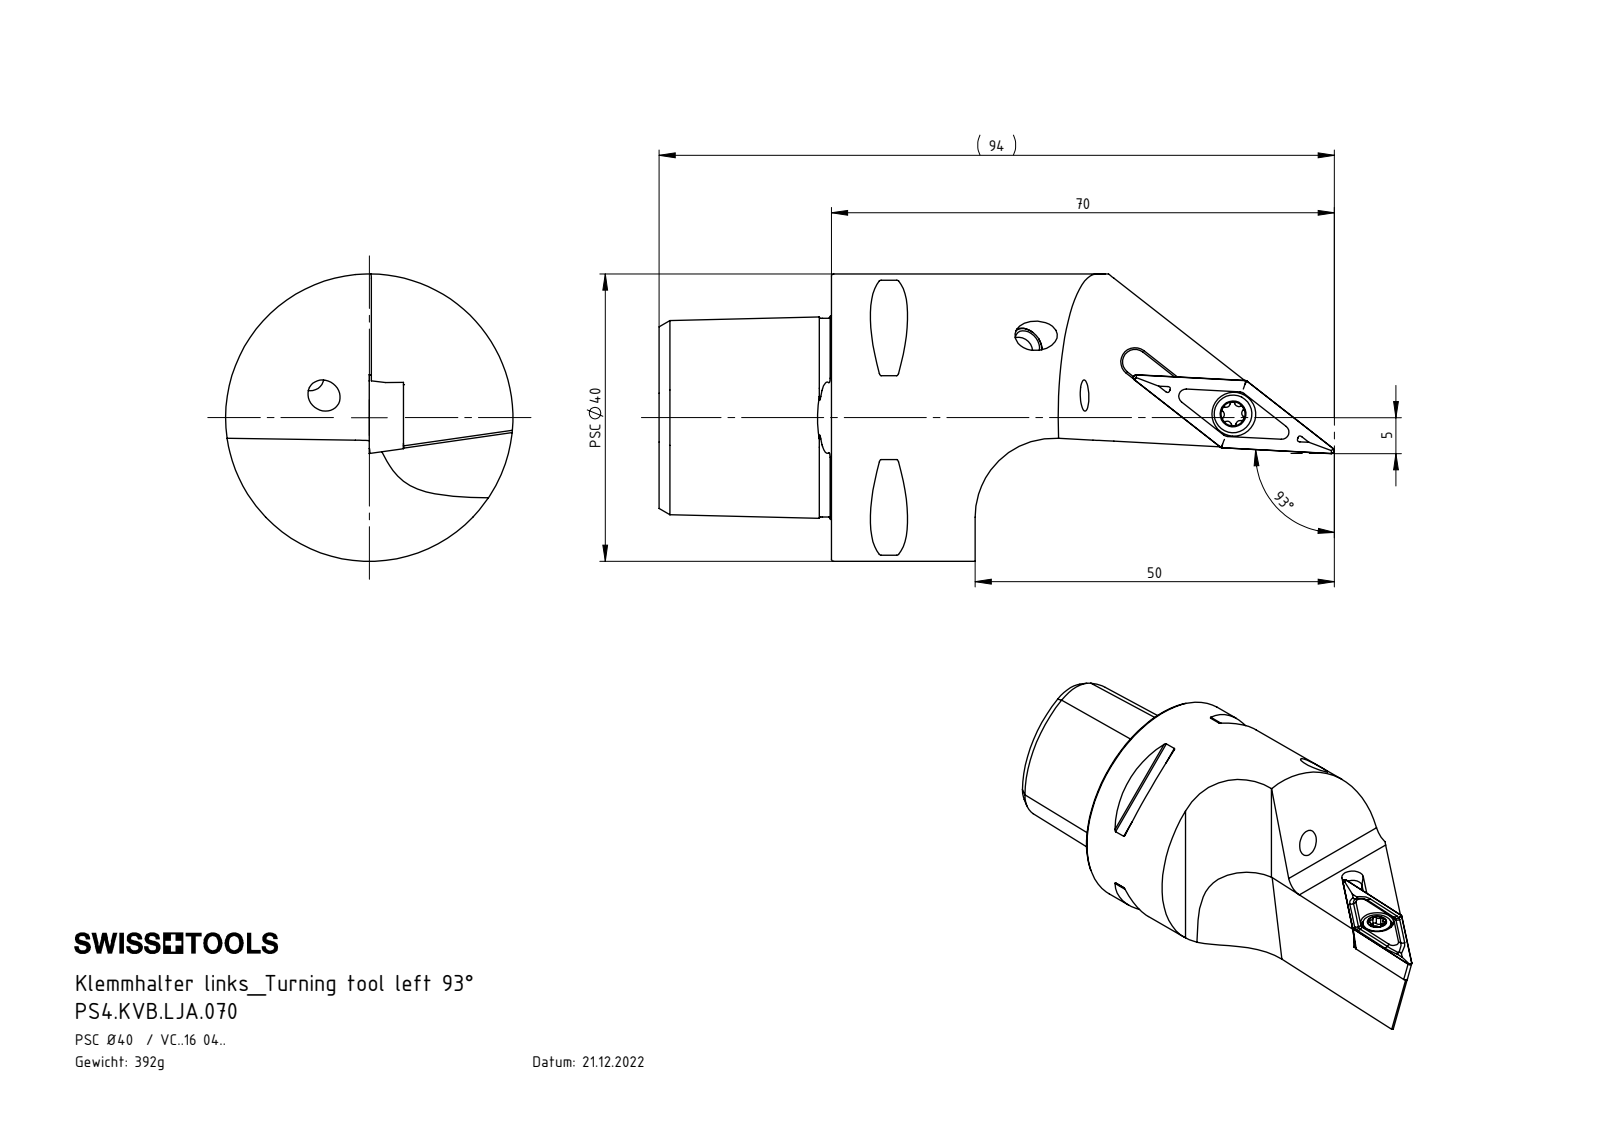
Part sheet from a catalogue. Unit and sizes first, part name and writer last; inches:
Units: inches
Overall size (bounding box): 3.701 × 1.575 × 1.575
Round holes (diameter × count): ⌀0.165 ×3, ⌀0.157 ×2, ⌀0.13 ×1, ⌀0.173 ×1, ⌀0.181 ×1, ⌀0.197 ×1, ⌀0.24 ×1, ⌀0.492 ×1, ⌀0.709 ×1, ⌀0.787 ×1
Round bosses / shafts (diameter × count): ⌀1.575 ×1, ⌀0.207 ×1, ⌀0.197 ×1, ⌀0.157 ×1
Partial cylindrical surfaces — rounded edges, fillets, slot ends (radius × count): R0.012 ×8, R0.013 ×6, R0.023 ×6, R0.118 ×2, R0.433 ×2, R0.069 ×1
Main face-to-face distances: 0.176, 0.945, 0.611, 1.732, 0.787, 1.39, 0.354, 0.591, 1.142, 0.187
Hole centre spacings: 0.925, 1.728, 1.733, 2.654, 2.658
Volume: 3.022 in³ · Surface area: 20.92 in²
Bodies: 5 solids, 283 faces (54 planar, 69 cylindrical, 160 other)
Part name (STEP PRODUCT): KVT_MB_600_050; PS4-KVB.LJA.070_A_Fertigbearbeitung; PS4.KVB.LJA.070; WCB-ER2.001.009_A (+1 more)
STEP written by: SolidWorks 2017 (AUTOMOTIVE_DESIGN)
